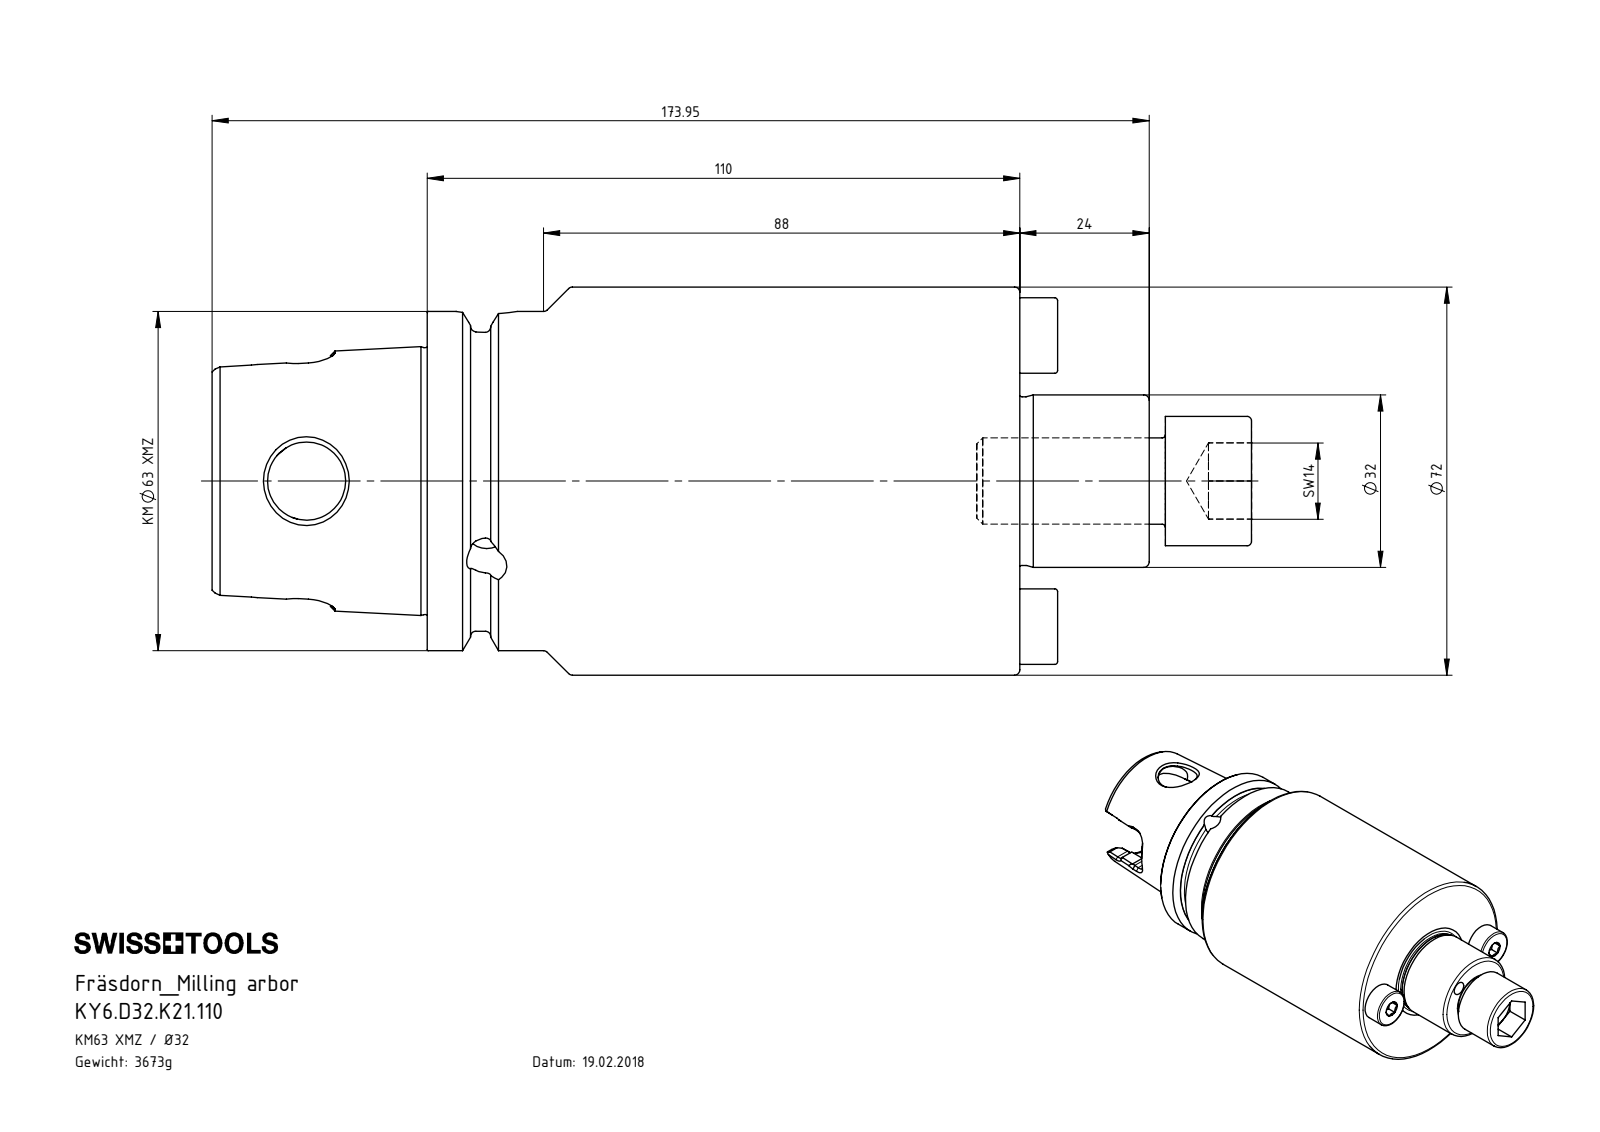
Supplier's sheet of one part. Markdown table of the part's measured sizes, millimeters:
| quantity | value |
| --- | --- |
| part name | D32-ER2.001.022_B; KY6-D32.K21.110_B; D32-ER1.002.035_A; KY6.D32.K21.110 |
| STEP written by | SolidWorks 2017 (CONFIG_CONTROL_DESIGN) |
| units | millimeters |
| bodies | 4 solids, 387 faces (86 planar, 102 cylindrical, 199 other) |
| overall size | 192.95 × 72 × 72 |
| volume | 467 847 mm³ |
| surface area | 56 584 mm² |
| round holes (diameter × count) | 5 × 5, 7.47 × 2, 12 × 2, 6.8 × 1, 8.48 × 1, 10 × 1, 11.5 × 1, 14 × 1, 14.5 × 1, 17 × 1, 31.1 × 1, 35.27 × 1 |
| round bosses / shafts (diameter × count) | 14 × 2, 6 × 2, 4.6 × 2, 72 × 1, 62.95 × 1, 55.7 × 1, 32 × 1, 31.3 × 1 |
| partial cylindrical surfaces (radius × count) | 4 × 8, 7.04 × 2 |
| main face-to-face distances | 110, 1.1, 111.1, 6, 3, 135.1, 134, 24, 32, 123 |
| hole center spacings | 12.25, 20.28, 27, 36.7, 24.49, 54 |
